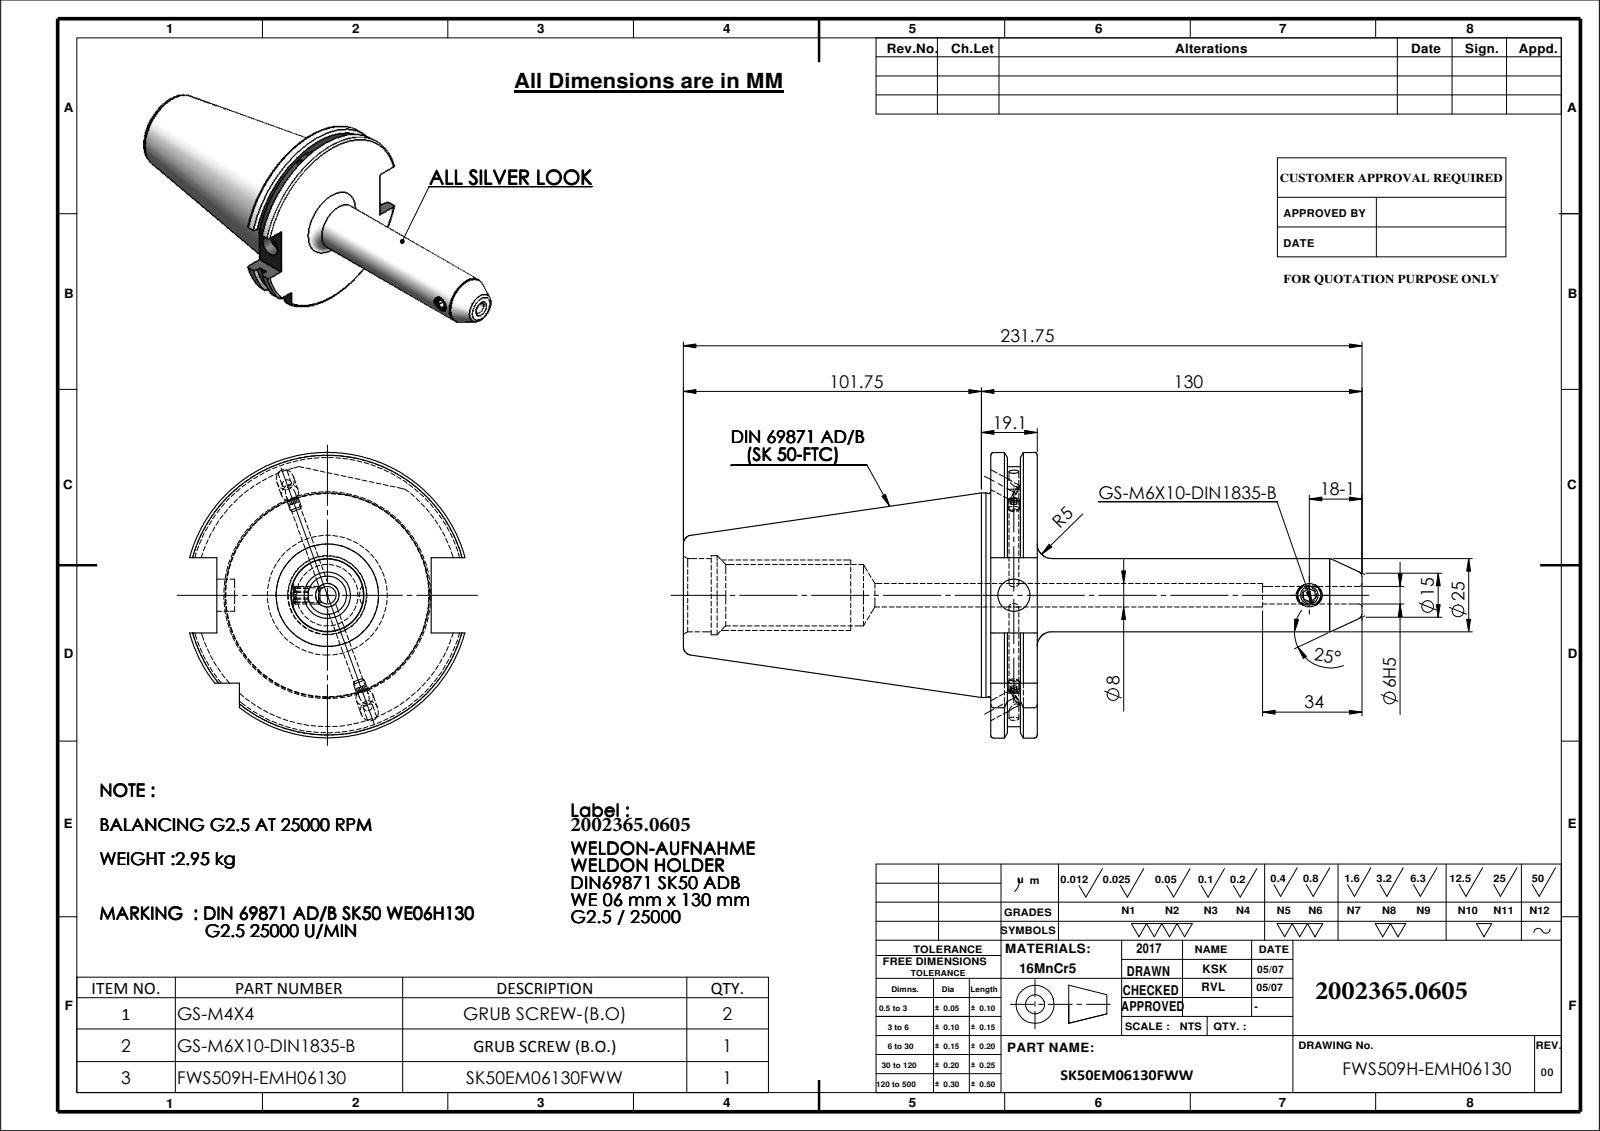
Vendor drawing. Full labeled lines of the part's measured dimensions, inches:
Part name (STEP PRODUCT): Copy of M4X4_DIN 913 - M4 x 4-N; SK50EM06130FWW; 91506-WE706130; M6X10._DIN 913 - M8 x 8-N
STEP written by: SolidWorks 2009 (CONFIG_CONTROL_DESIGN)
Units: inches
Bodies: 4 solids, 165 faces (51 planar, 53 cylindrical, 61 other)
Overall size (bounding box): 9.124 × 3.839 × 3.703
Volume: 23.37 in³ · Surface area: 84.27 in²
Round holes (diameter × count): ⌀0.236 ×3, ⌀0.315 ×2, ⌀0.13 ×1, ⌀0.197 ×1, ⌀0.433 ×1, ⌀0.827 ×1, ⌀0.984 ×1, ⌀1.063 ×1
Round bosses / shafts (diameter × count): ⌀0.157 ×2, ⌀2.75 ×1, ⌀2.734 ×1, ⌀0.236 ×1
Partial cylindrical surfaces — rounded edges, fillets, slot ends (radius × count): R1.768 ×1, R1.919 ×1
Main face-to-face distances: 0.626, 0.4, 0.226, 0.223, 0.177, 0.403, 4.132, 4.355, 4.531, 4.758
Hole centre spacings: 3.972
